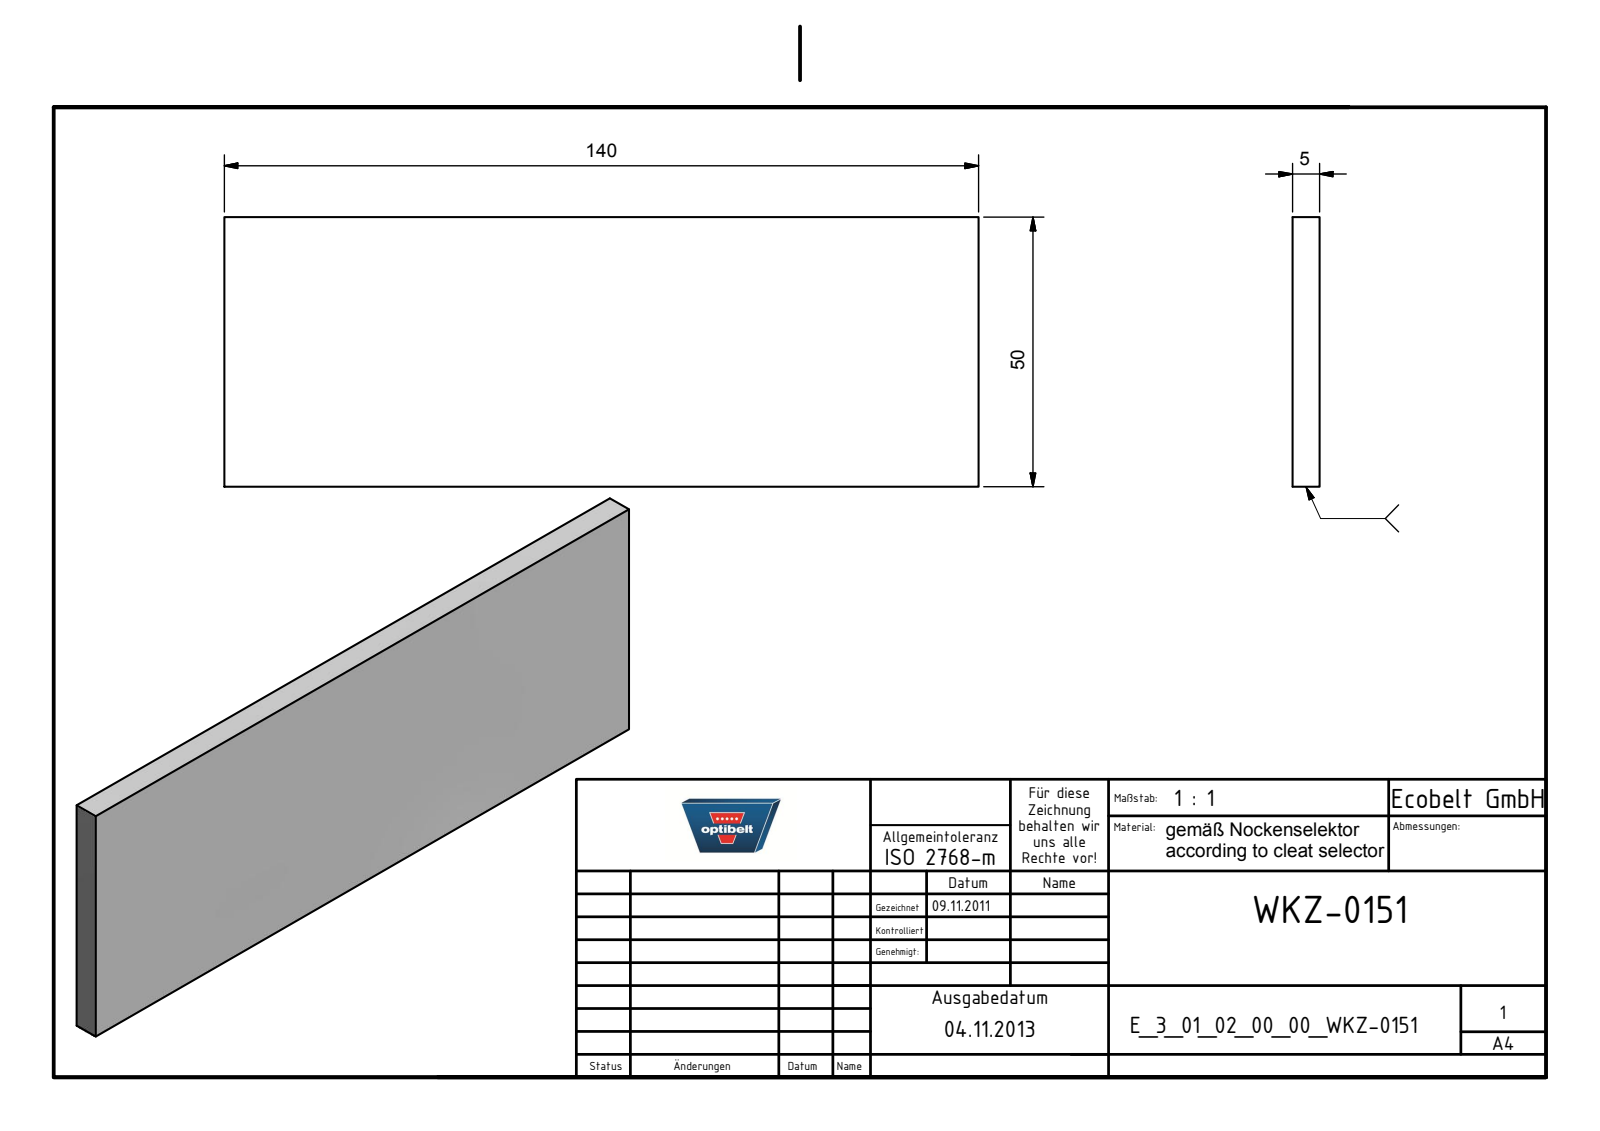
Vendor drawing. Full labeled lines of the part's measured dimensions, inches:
Part name (STEP PRODUCT): E_3_01_02_00_00_WKZ-0151
STEP written by: Autodesk Inventor 2021 (AUTOMOTIVE_DESIGN)
Units: inches
Bodies: 1 solid, 6 faces (6 planar, 0 cylindrical, 0 other)
Overall size (bounding box): 5.512 × 1.969 × 0.197
Volume: 2.136 in³ · Surface area: 24.65 in²
Main face-to-face distances: 0.197, 1.969, 5.512
